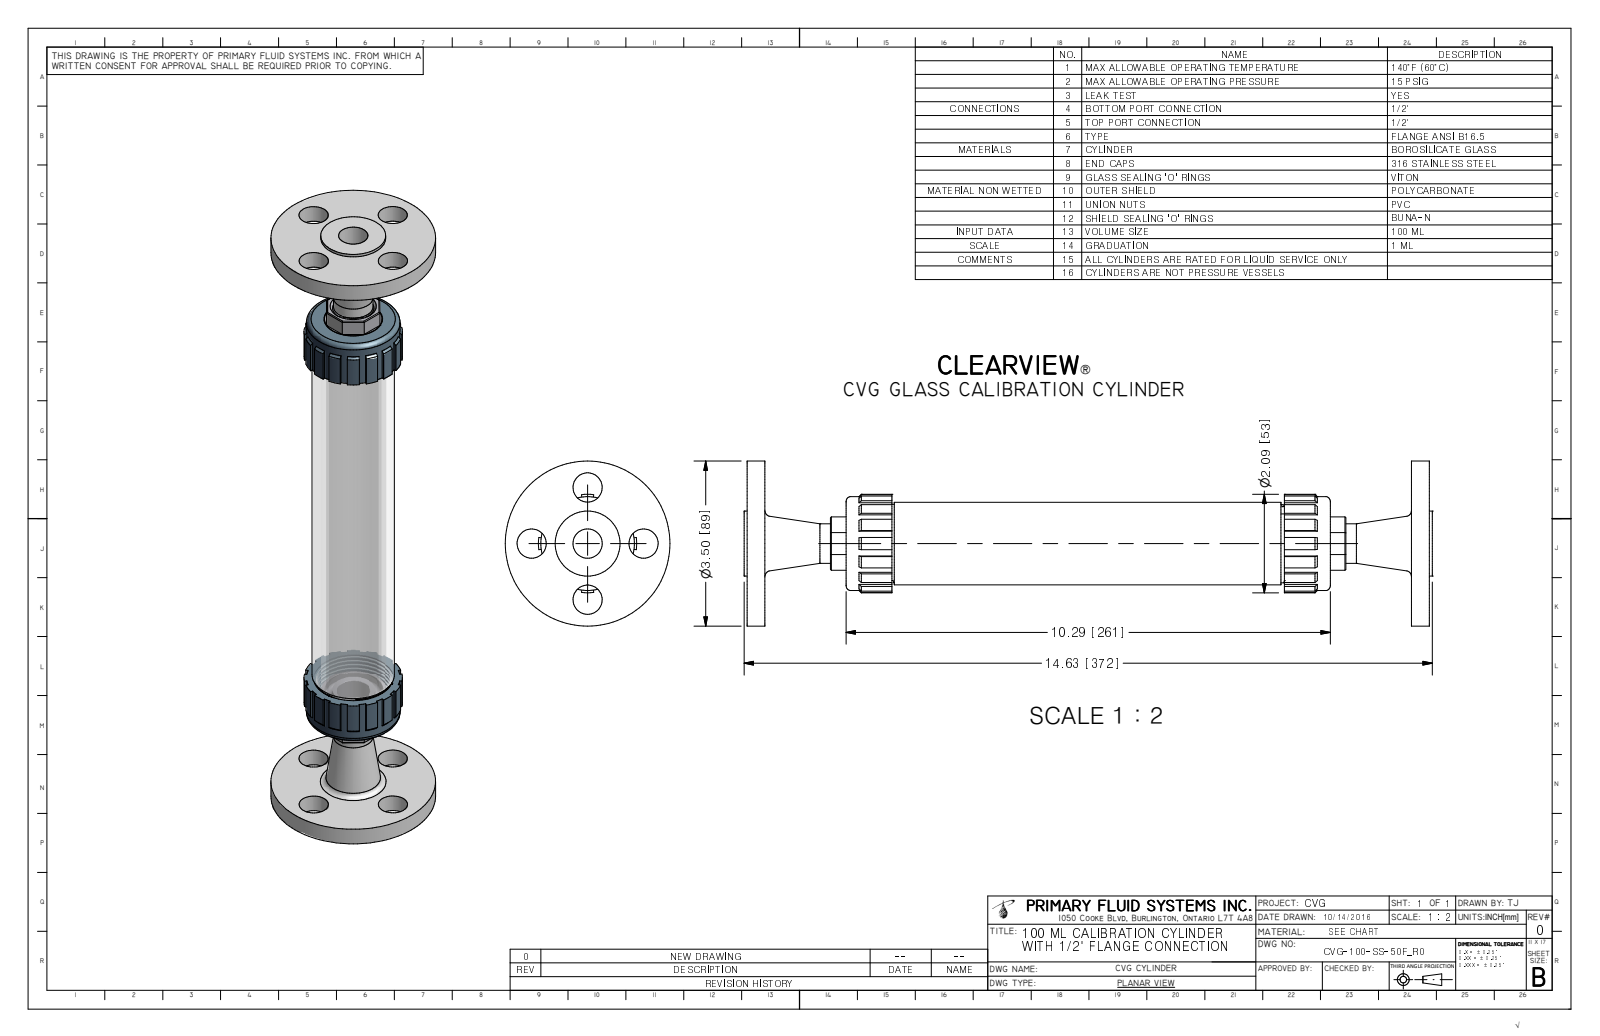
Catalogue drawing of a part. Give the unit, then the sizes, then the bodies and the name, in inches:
Units: inches
Overall size (bounding box): 14.629 × 3.5 × 3.5
Round holes (diameter × count): ⌀0.62 ×4, ⌀0.622 ×1, ⌀0.703 ×1, ⌀0.88 ×1, ⌀1.071 ×1, ⌀1.25 ×1, ⌀1.4 ×1, ⌀1.663 ×1
Round bosses / shafts (diameter × count): ⌀3.5 ×1, ⌀1.75 ×1, ⌀1.565 ×1, ⌀1.5 ×1, ⌀1.38 ×1, ⌀1.36 ×1, ⌀1.3 ×1, ⌀1.225 ×1
Partial cylindrical surfaces — rounded edges, fillets, slot ends (radius × count): R1.045 ×1
Main face-to-face distances: 0.38, 14.124, 14.504, 13.744, 0.063, 0.443, 14.187, 14.567, 14.63, 2.368
Hole centre spacings: 1.19, 1.683, 2.38
Volume: 21.66 in³ · Surface area: 285.1 in²
Bodies: 8 solids, 370 faces (128 planar, 58 cylindrical, 184 other)
Part name (STEP PRODUCT): CVG-100-SS-50F_R0; CVG-3-100-METAL-S-50_R1; CVG-6-100; CVG-1-100-A_R0 (+2 more)
STEP written by: Autodesk Inventor 2009 (AUTOMOTIVE_DESIGN)
